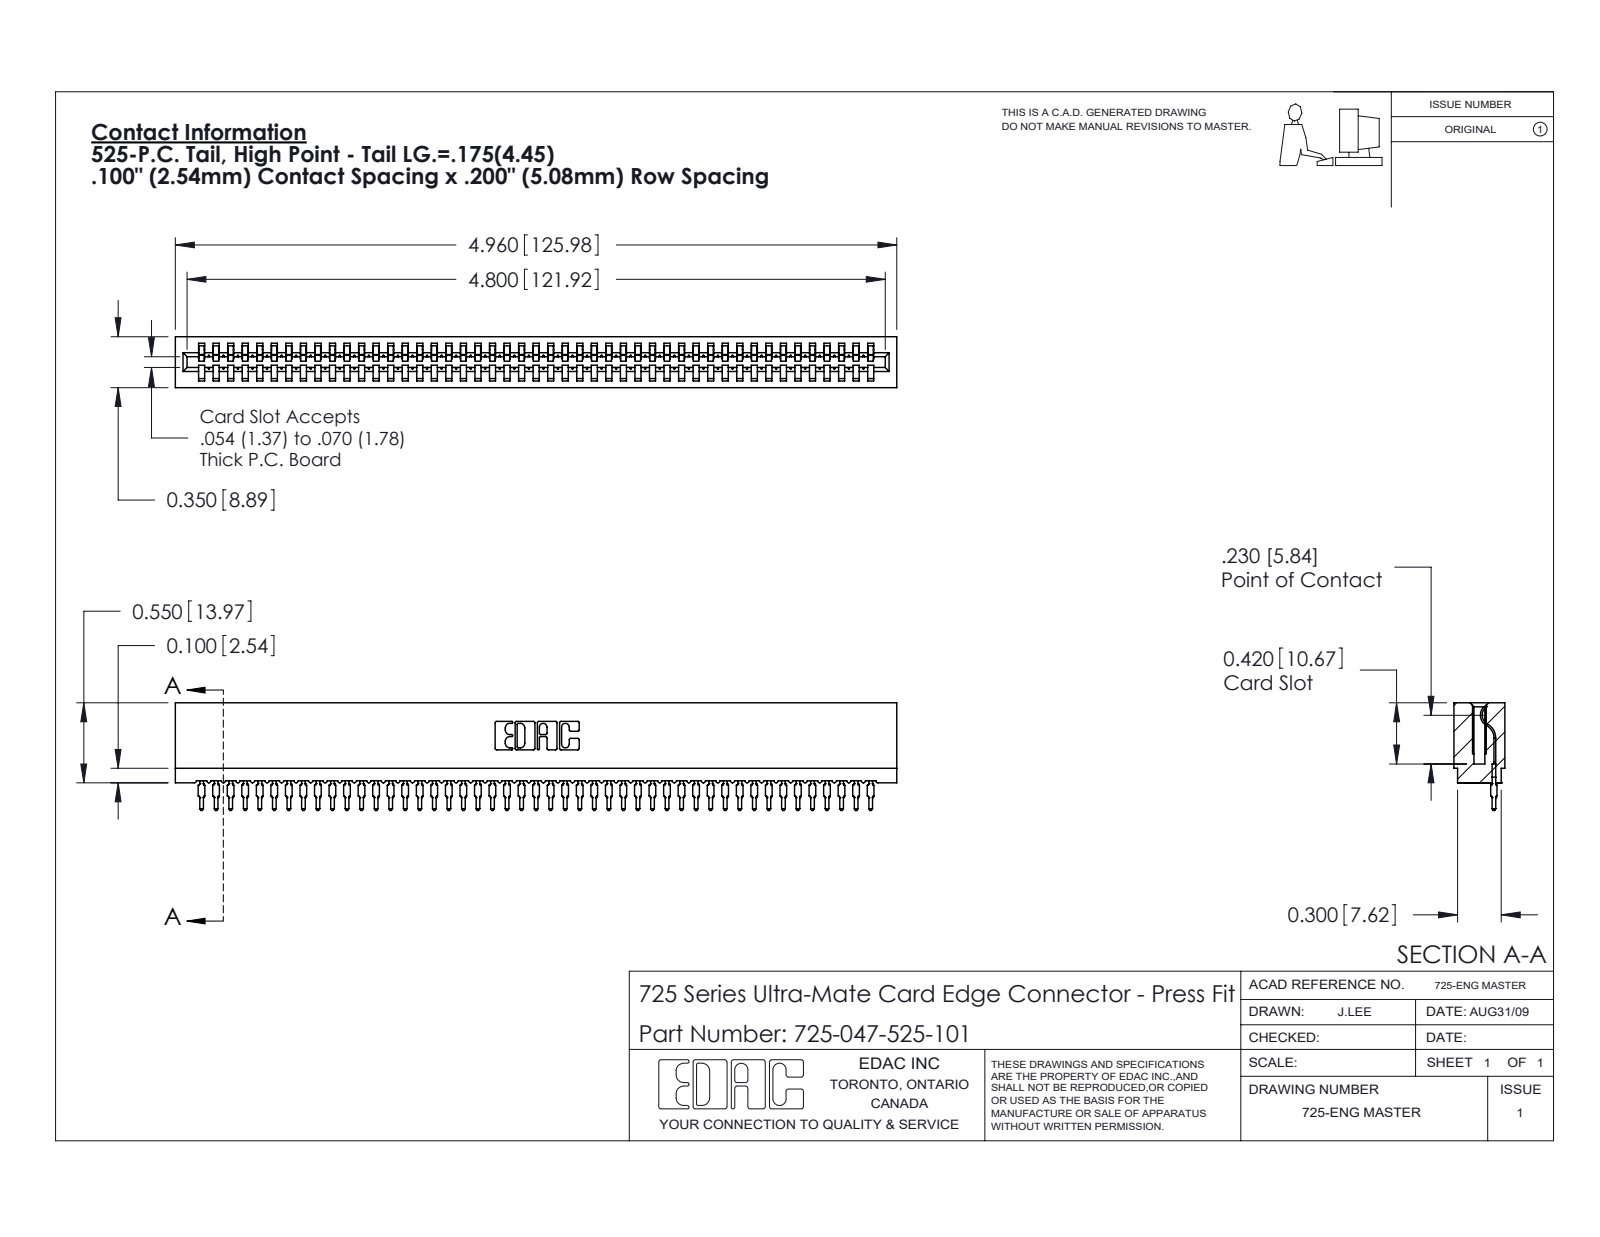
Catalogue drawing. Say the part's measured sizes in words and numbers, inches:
The part is named "725-047-525-101; 725 Part_Insulator Option - 01; 745-292-001_525". Its 3-D file was written by "SolidWorks 2020 (CONFIG_CONTROL_DESIGN)". It is 48 solids with 5359 faces: 3204 planar, 933 cylindrical and 1222 other. Overall it measures 4.96 by 0.741 by 0.35 inches. Its volume is 0.579 cubic inches and its surface area 28.32 square inches. Partial cylindrical surfaces (rounded edges, fillets, slot ends): 94 of radius 0.015, 94 of radius 0.021, 22 of radius 0.01, 6 of radius 0.007, 6 of radius 0.031, 4 of radius 0.005, 4 of radius 0.011, 3 of radius 0.026. The main face-to-face distances are 0.35, 0.2, 0.212, 0.138, 0.1, 0.045, 0.305, 0.093, 0.167, 0.063.
